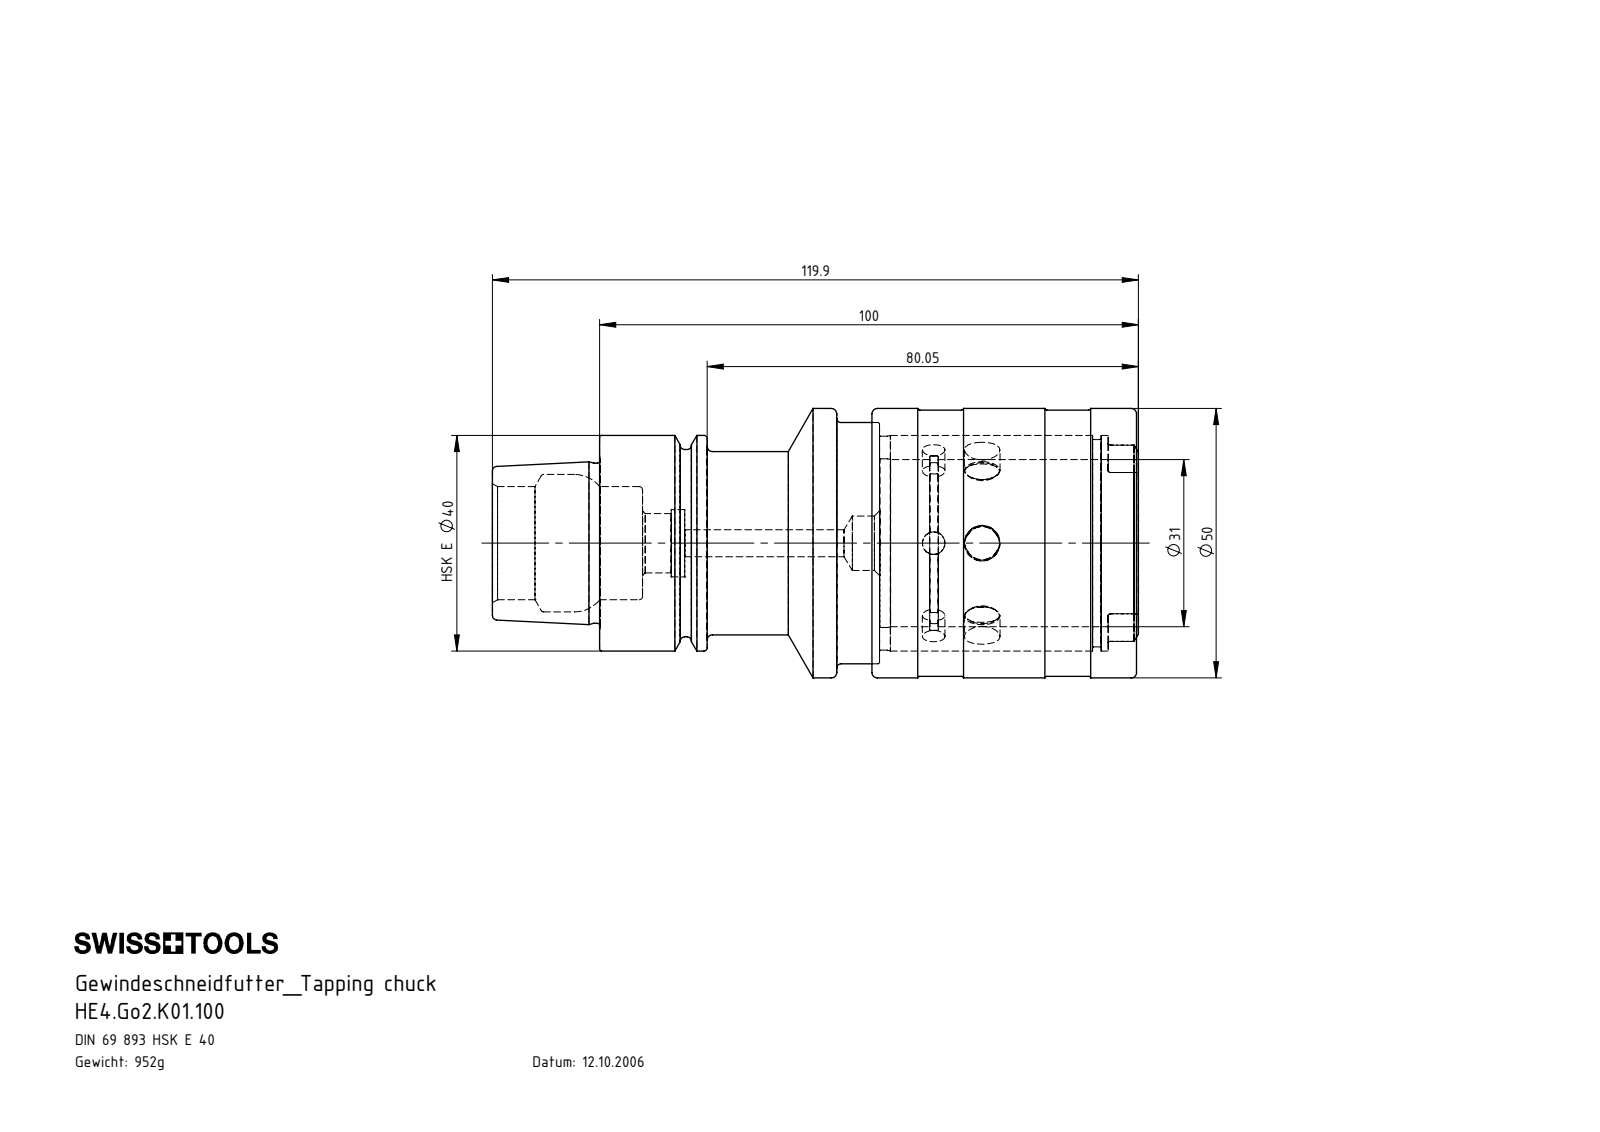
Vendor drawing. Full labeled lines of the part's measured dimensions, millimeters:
Part name (STEP PRODUCT): HE4.Go2.K01.100; Einbausatz Go2_gespannt; Kugel Go2; Hülse Go2 (+6 more)
STEP written by: SolidWorks 2011 (AUTOMOTIVE_DESIGN)
Units: millimetres
Bodies: 10 solids, 301 faces (51 planar, 99 cylindrical, 151 other)
Overall size (bounding box): 119.9 × 50 × 50
Volume: 121 142 mm³ · Surface area: 49 871 mm²
Round holes (diameter × count): ⌀4.2 ×3, ⌀6.6 ×3, ⌀2.5 ×1, ⌀5 ×1, ⌀10.1 ×1, ⌀11 ×1, ⌀12.5 ×1, ⌀21 ×1, ⌀25.5 ×1, ⌀31 ×1, ⌀31.3 ×1, ⌀32.35 ×1
Round bosses / shafts (diameter × count): ⌀50 ×1, ⌀49.4 ×1, ⌀44.75 ×1, ⌀40 ×1, ⌀39.7 ×1, ⌀38.45 ×1, ⌀34.75 ×1, ⌀34 ×1
Partial cylindrical surfaces — rounded edges, fillets, slot ends (radius × count): R3.1 ×3, R0.5 ×2
Main face-to-face distances: 12, 12.65, 0.65, 0.7, 12.7, 14.6, 14.55, 13.9, 1.9, 51.95
Hole centre spacings: 9
